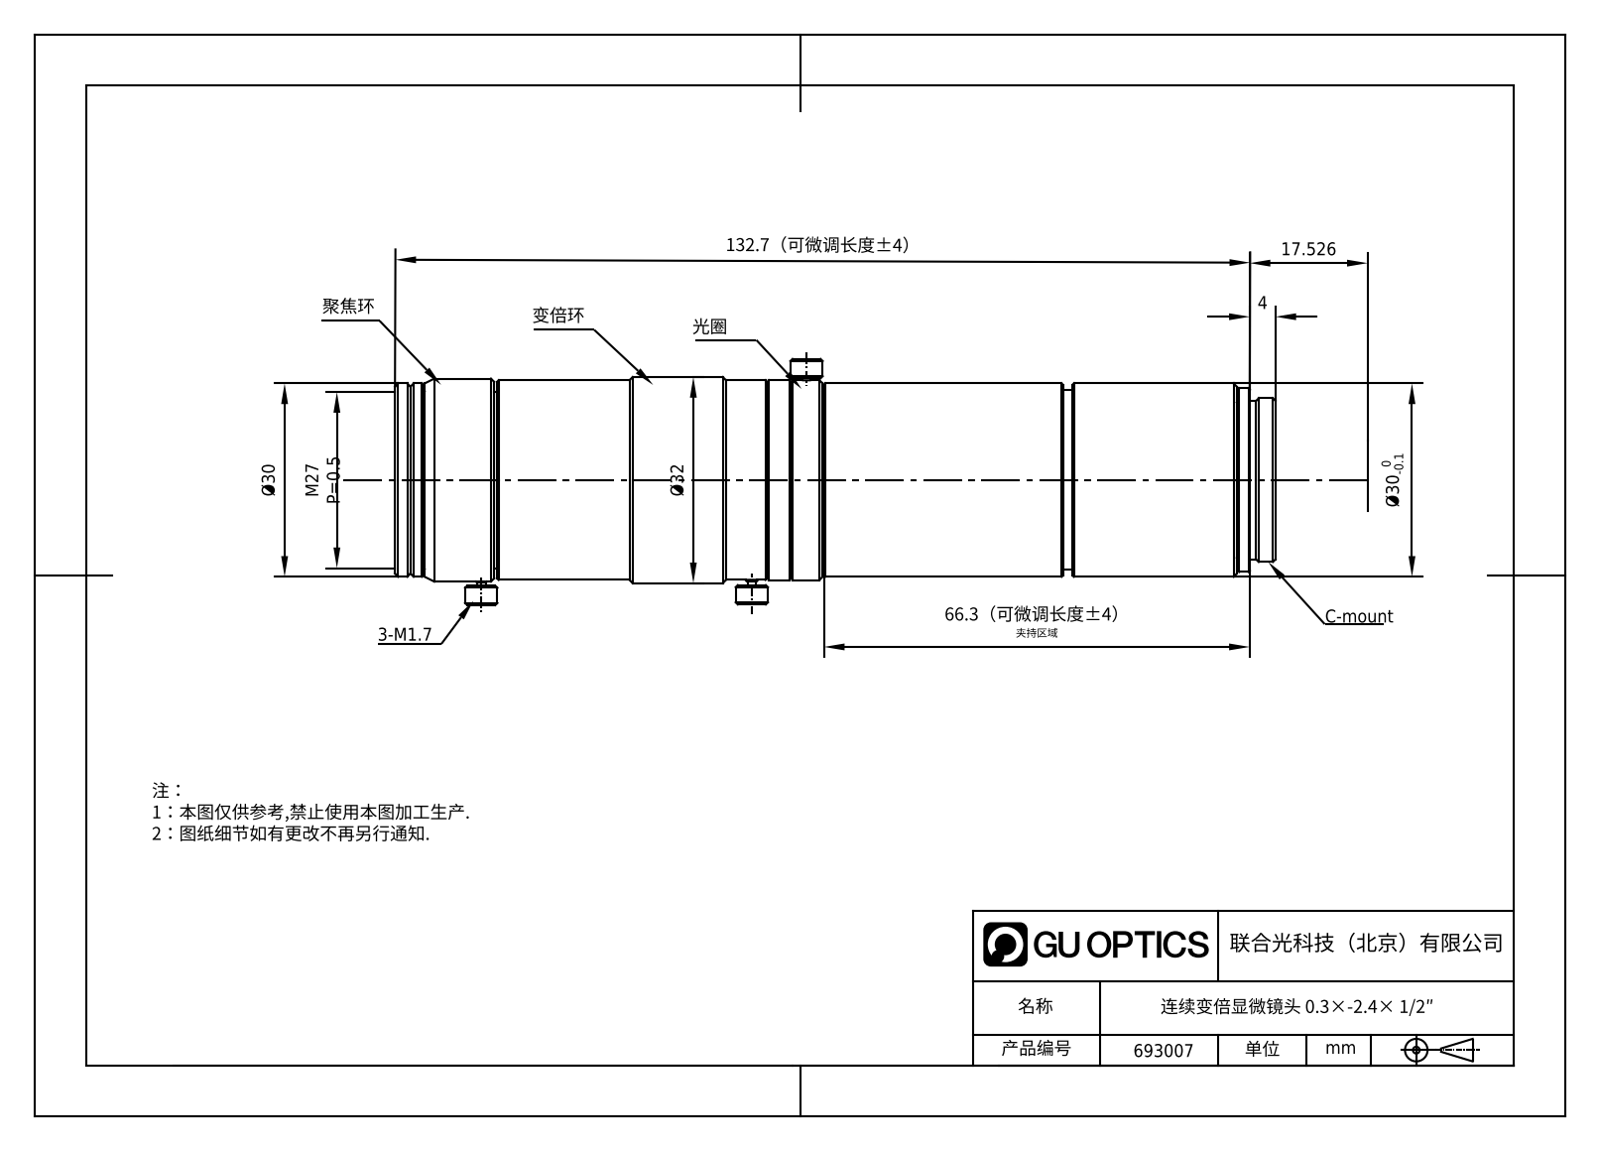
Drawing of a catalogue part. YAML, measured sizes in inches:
part_name: "VSZ-0324S"
step_written_by: "SolidWorks 2020 (AUTOMOTIVE_DESIGN)"
units: inches
bodies: {solids: 1, faces: 176, planar: 28, cylindrical: 56, other: 92}
overall_size: [5.382, 1.504, 1.259]
volume: 5.74
surface_area: 27.24
round_holes:
  - {diameter: 0.669, count: 1}
  - {diameter: 0.768, count: 1}
  - {diameter: 0.846, count: 1}
  - {diameter: 1.043, count: 1}
  - {diameter: 1.063, count: 1}
round_bosses_or_shafts:
  - {diameter: 0.197, count: 3}
  - {diameter: 0.053, count: 3}
  - {diameter: 1.259, count: 1}
  - {diameter: 1.24, count: 1}
  - {diameter: 1.22, count: 1}
  - {diameter: 1.22, count: 1}
  - {diameter: 1.181, count: 1}
  - {diameter: 1.122, count: 1}
face_to_face_distances: [4.598, 0.02, 2.728, 0.335, 0.059, 1.811, 0.256, 2.61, 0.197, 2.531]
